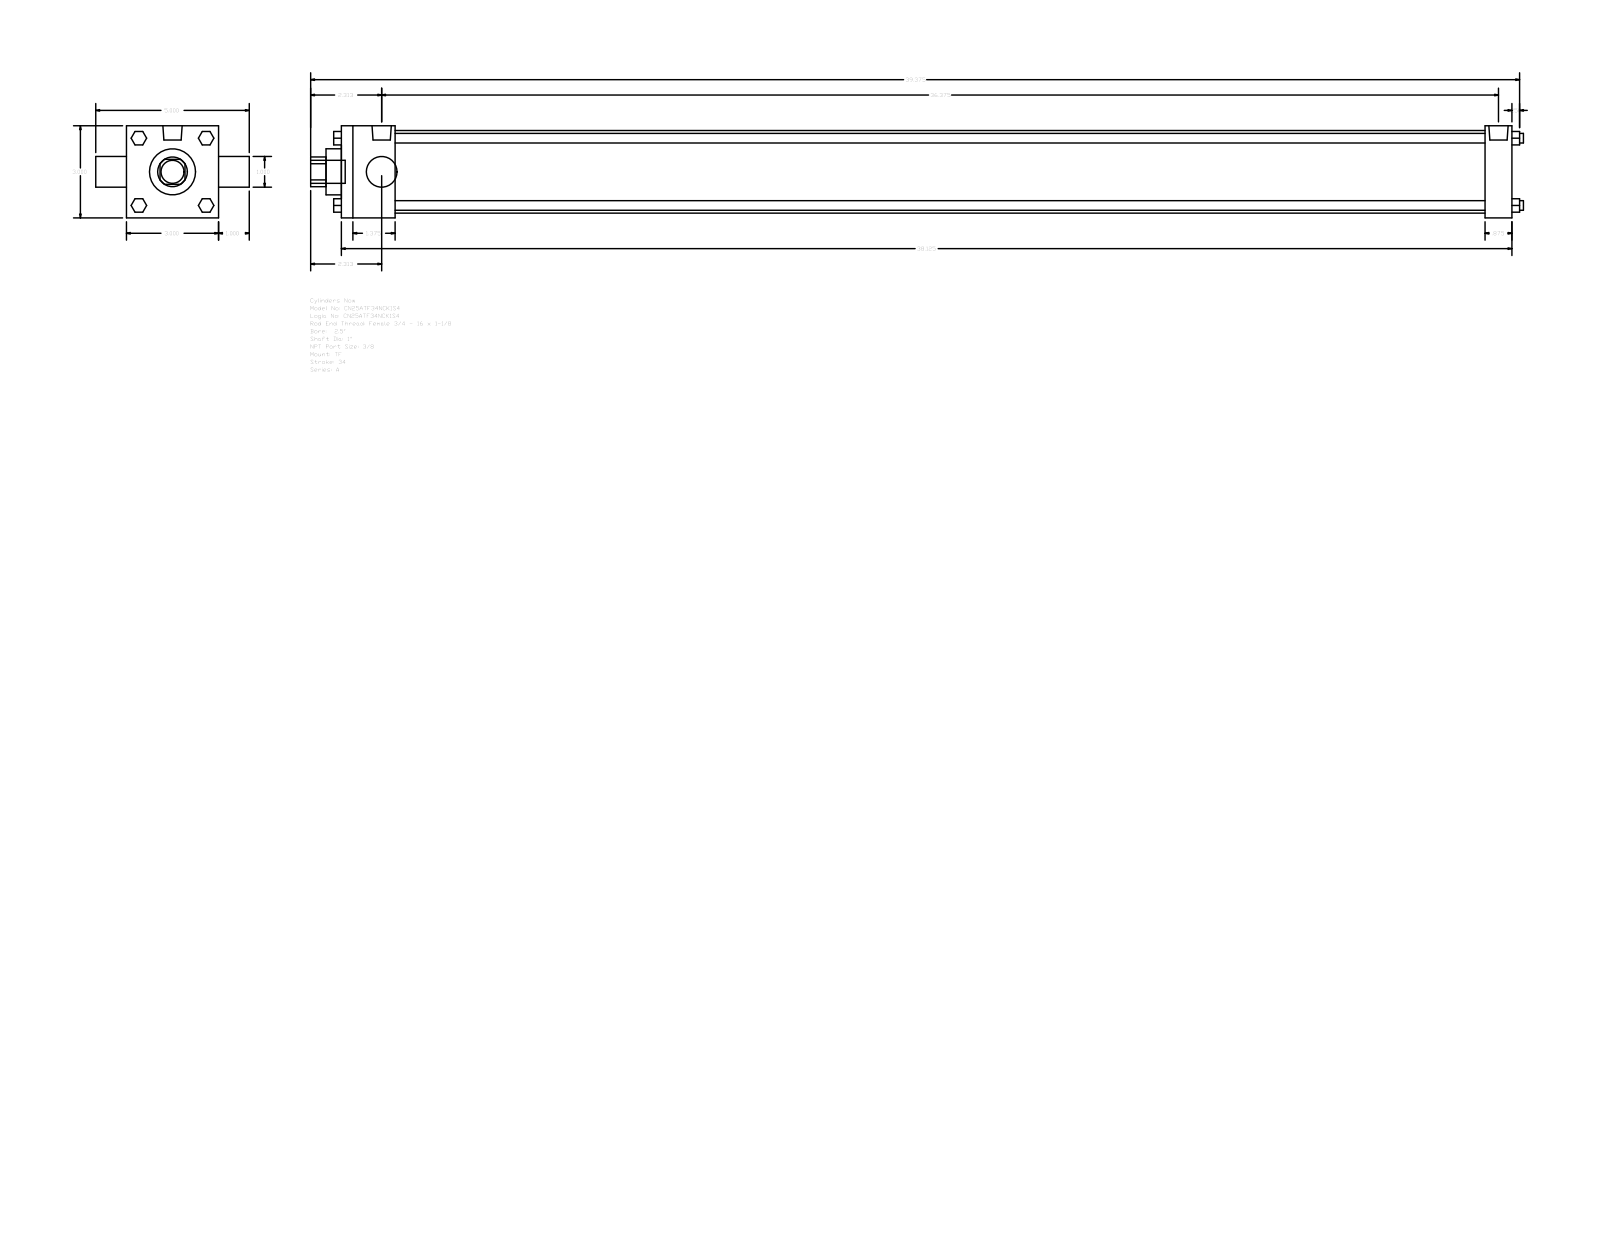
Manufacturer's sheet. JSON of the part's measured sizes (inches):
{"part_name": "A_TF__0250_1", "step_written_by": "GSSL Pune (CONFIG_CONTROL_DESIGN)", "units": "inches", "bodies": {"solids": 0, "faces": 120, "planar": 92, "cylindrical": 28, "other": 0}, "overall_size": [39.5, 5, 3], "round_holes": [[1, 2], [1.5, 1], [2.69, 1]], "round_bosses_or_shafts": [[0.313, 4], [0.219, 3], [0.627, 2], [0.75, 1]], "partial_cylinders_radius": [[0.484, 1]], "face_to_face_distances": [3, 38.125, 1.75, 37.25, 35.5, 36.375, 0.875, 1, 4, 38.625]}
